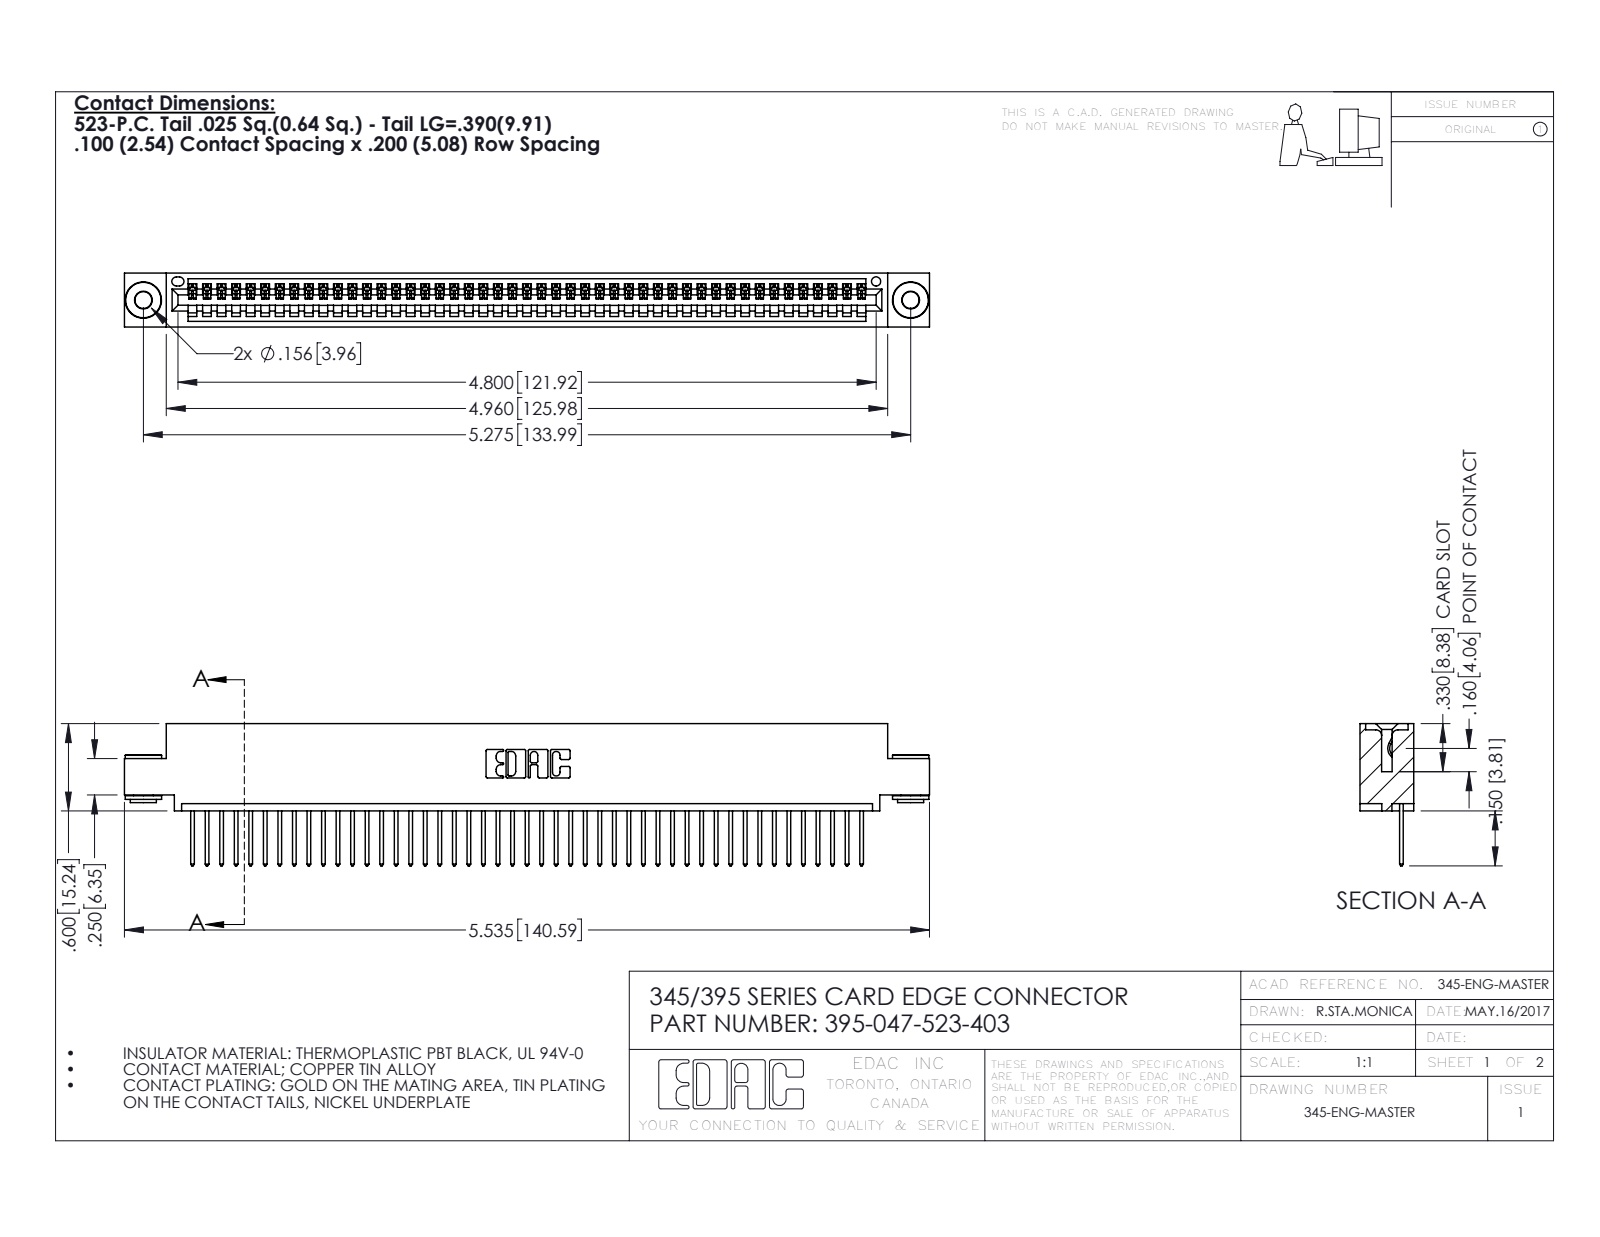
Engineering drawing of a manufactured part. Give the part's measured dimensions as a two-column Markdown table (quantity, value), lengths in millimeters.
| quantity | value |
| --- | --- |
| part name | 345-250-002_345-250-002-102; 345 Part_0.110 Offset - 0.156 Dia-TH; 345-292-001_345-293-123; 395-047-523-403 |
| STEP written by | SolidWorks 2016 (CONFIG_CONTROL_DESIGN) |
| units | millimeters |
| bodies | 50 solids, 2894 faces (1974 planar, 912 cylindrical, 8 other) |
| overall size | 140.6 × 24.8 × 9.4 |
| volume | 13 300 mm³ |
| surface area | 18 120 mm² |
| round holes (diameter × count) | 2.9 × 2, 4 × 2, 1.6 × 1 |
| round bosses / shafts (diameter × count) | 6.4 × 2, 4.6 × 2, 3.5 × 2 |
| partial cylindrical surfaces (radius × count) | 0.2 × 94, 0.3 × 94, 0.3 × 22, 0.2 × 6, 0.8 × 6, 0.7 × 3, 0.8 × 2, 1 × 2 |
| main face-to-face distances | 1.8, 7.6, 9.4, 0.6, 5.1, 2.5, 6.9, 5.7, 3.8, 1.8 |
| hole center spacings | 6.9, 128, 134 |
